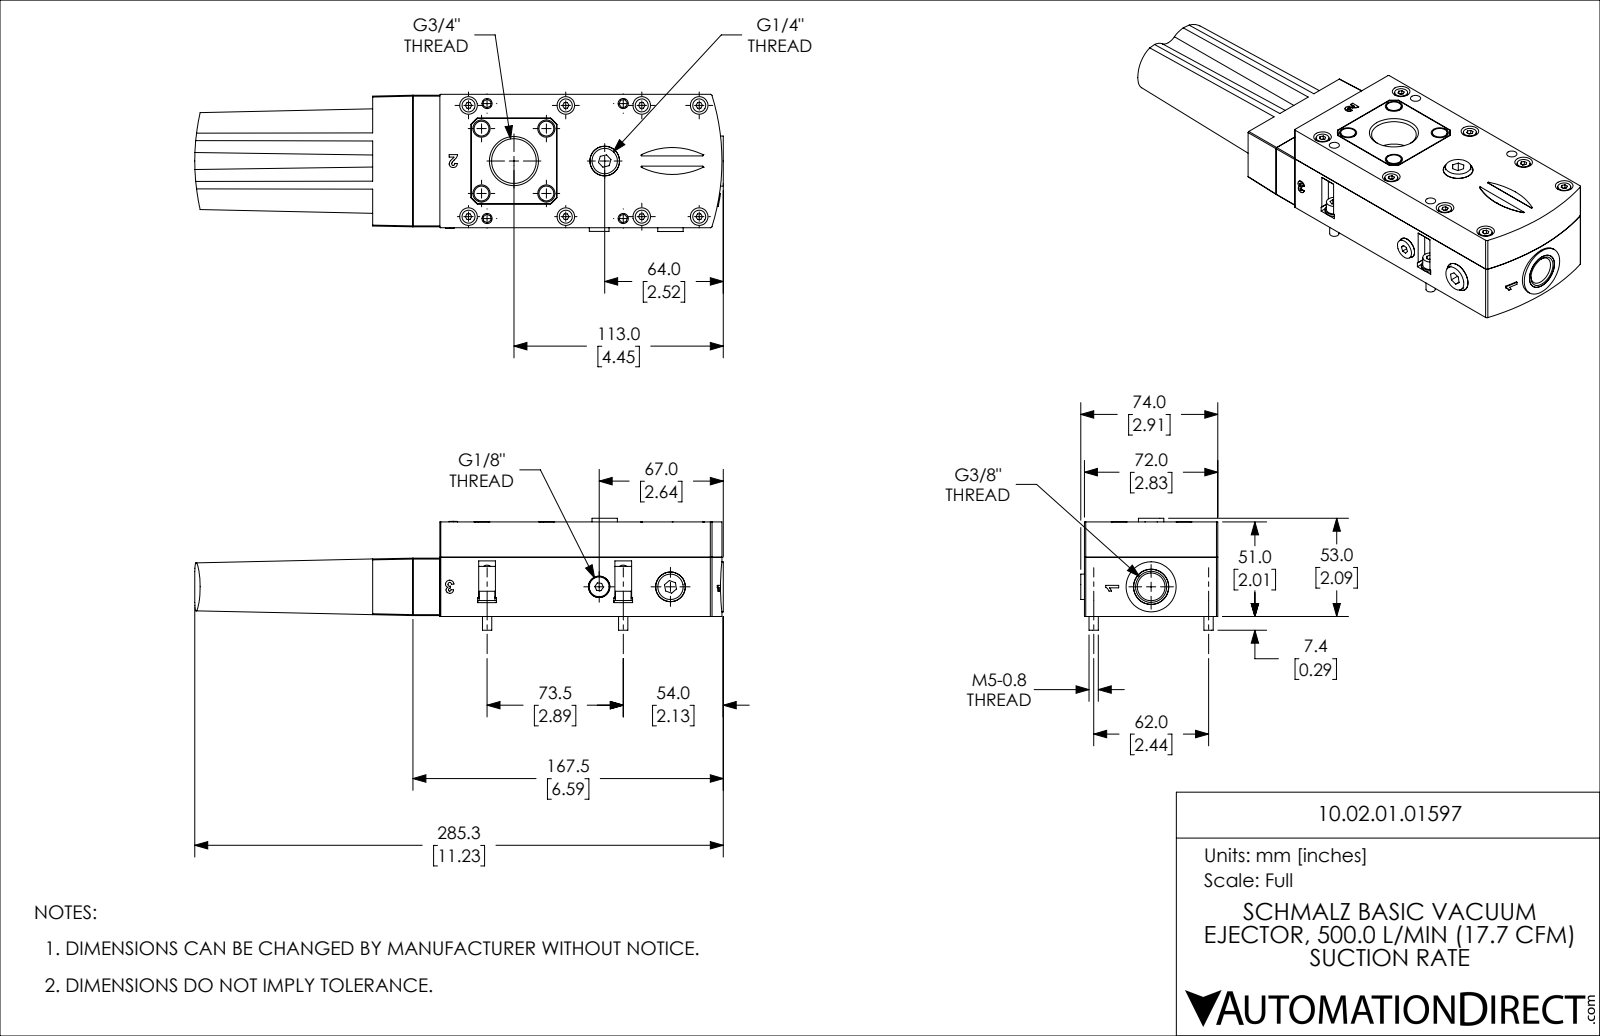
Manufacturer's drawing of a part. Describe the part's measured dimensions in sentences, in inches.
The part is named "10.02.01.01597". Its 3-D file was written by "SolidWorks 2021 (CONFIG_CONTROL_DESIGN)". It is 43 solids with 899 faces: 413 planar, 398 cylindrical and 88 other. Overall it measures 11.23 by 2.913 by 2.378 inches. Its volume is 43.95 cubic inches and its surface area 223.8 square inches. Round holes: 12 of diameter 0.177, 9 of diameter 0.374, 8 of diameter 0.13, 8 of diameter 0.244, 8 of diameter 0.256, 4 of diameter 0.138, 4 of diameter 0.169, 4 of diameter 0.209, 4 of diameter 0.217, 3 of diameter 0.453, 2 of diameter 0.173, 2 of diameter 0.315. Round bosses or shafts: 10 of diameter 0.276, 10 of diameter 0.157, 8 of diameter 0.236, 4 of diameter 0.394, 4 of diameter 0.335, 4 of diameter 0.315, 4 of diameter 0.197, 4 of diameter 0.111. Partial cylindrical surfaces (rounded edges, fillets, slot ends): 14 of radius 0.02, 8 of radius 0.181, 4 of radius 0.177, 4 of radius 0.199, 2 of radius 0.013, 2 of radius 0.013, 2 of radius 0.039, 2 of radius 0.373. The main face-to-face distances are 1.26, 0.748, 2.008, 2.835, 0.571, 0.02, 1.24, 0.157, 1.248, 1.996. The hole center spacings are 1.371, 1.364, 0.396, 0.964, 0.974, 1.33, 1.378, 1.939.
